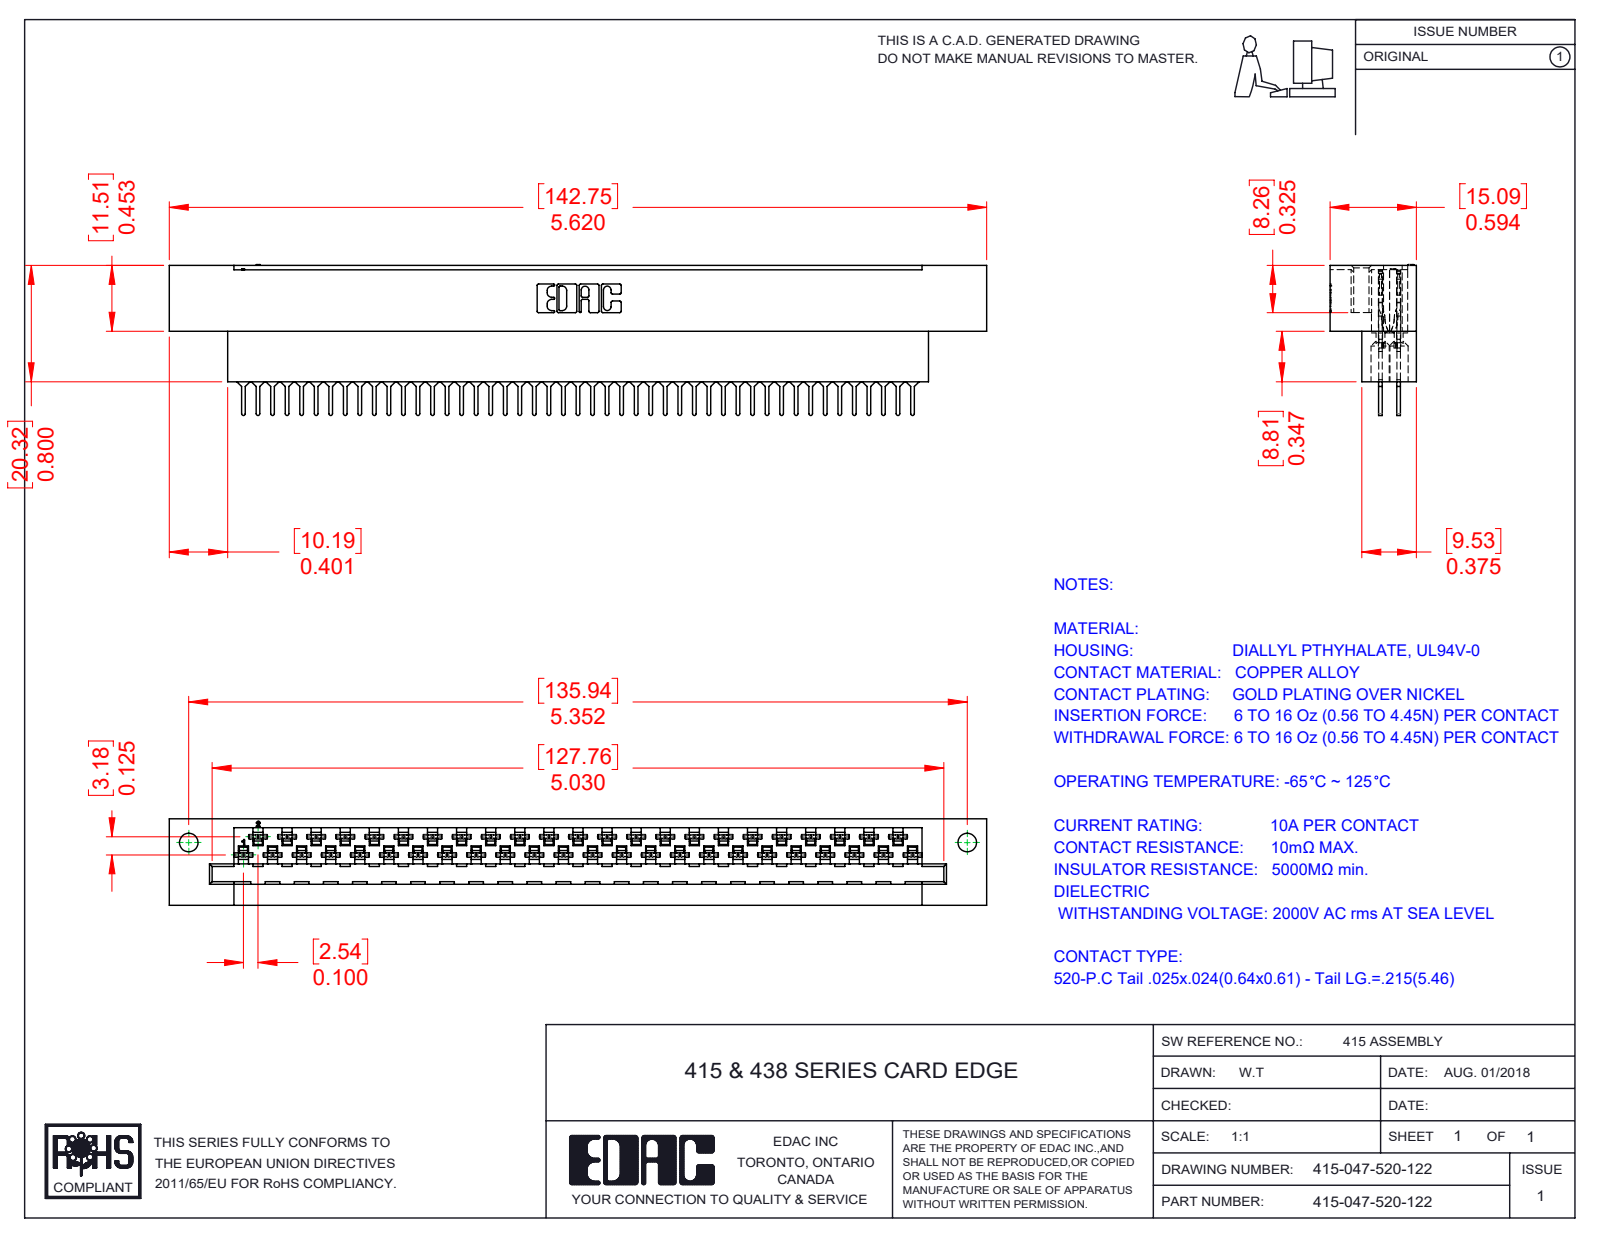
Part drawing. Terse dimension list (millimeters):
name: 415-047-520-122; 516-290-001_520; 415-210-001_415-210-047-122
written by: SolidWorks 2016 (CONFIG_CONTROL_DESIGN)
unit: mm
bodies: 48 solids, 4750 faces (3039 planar, 1266 cylindrical, 445 other)
size: 142.75 × 26.32 × 15.09
volume: 25 751 mm³; area: 30 070 mm²
holes: 47× ⌀1.27, 47× ⌀3.3, 2× ⌀3.25
rounds: 188× R0.3, 188× R0.56, 94× R0.18, 94× R0.2, 94× R0.41, 94× R2.03, 47× R0.32, 22× R0.25
face distances: 3.18, 0.61, 1.27, 1.88, 15.09, 1.94, 0.67, 6.61, 8.48, 6
hole spacings: 5.08, 10.16, 15.24, 20.32, 25.4, 30.48, 35.56, 2.54
